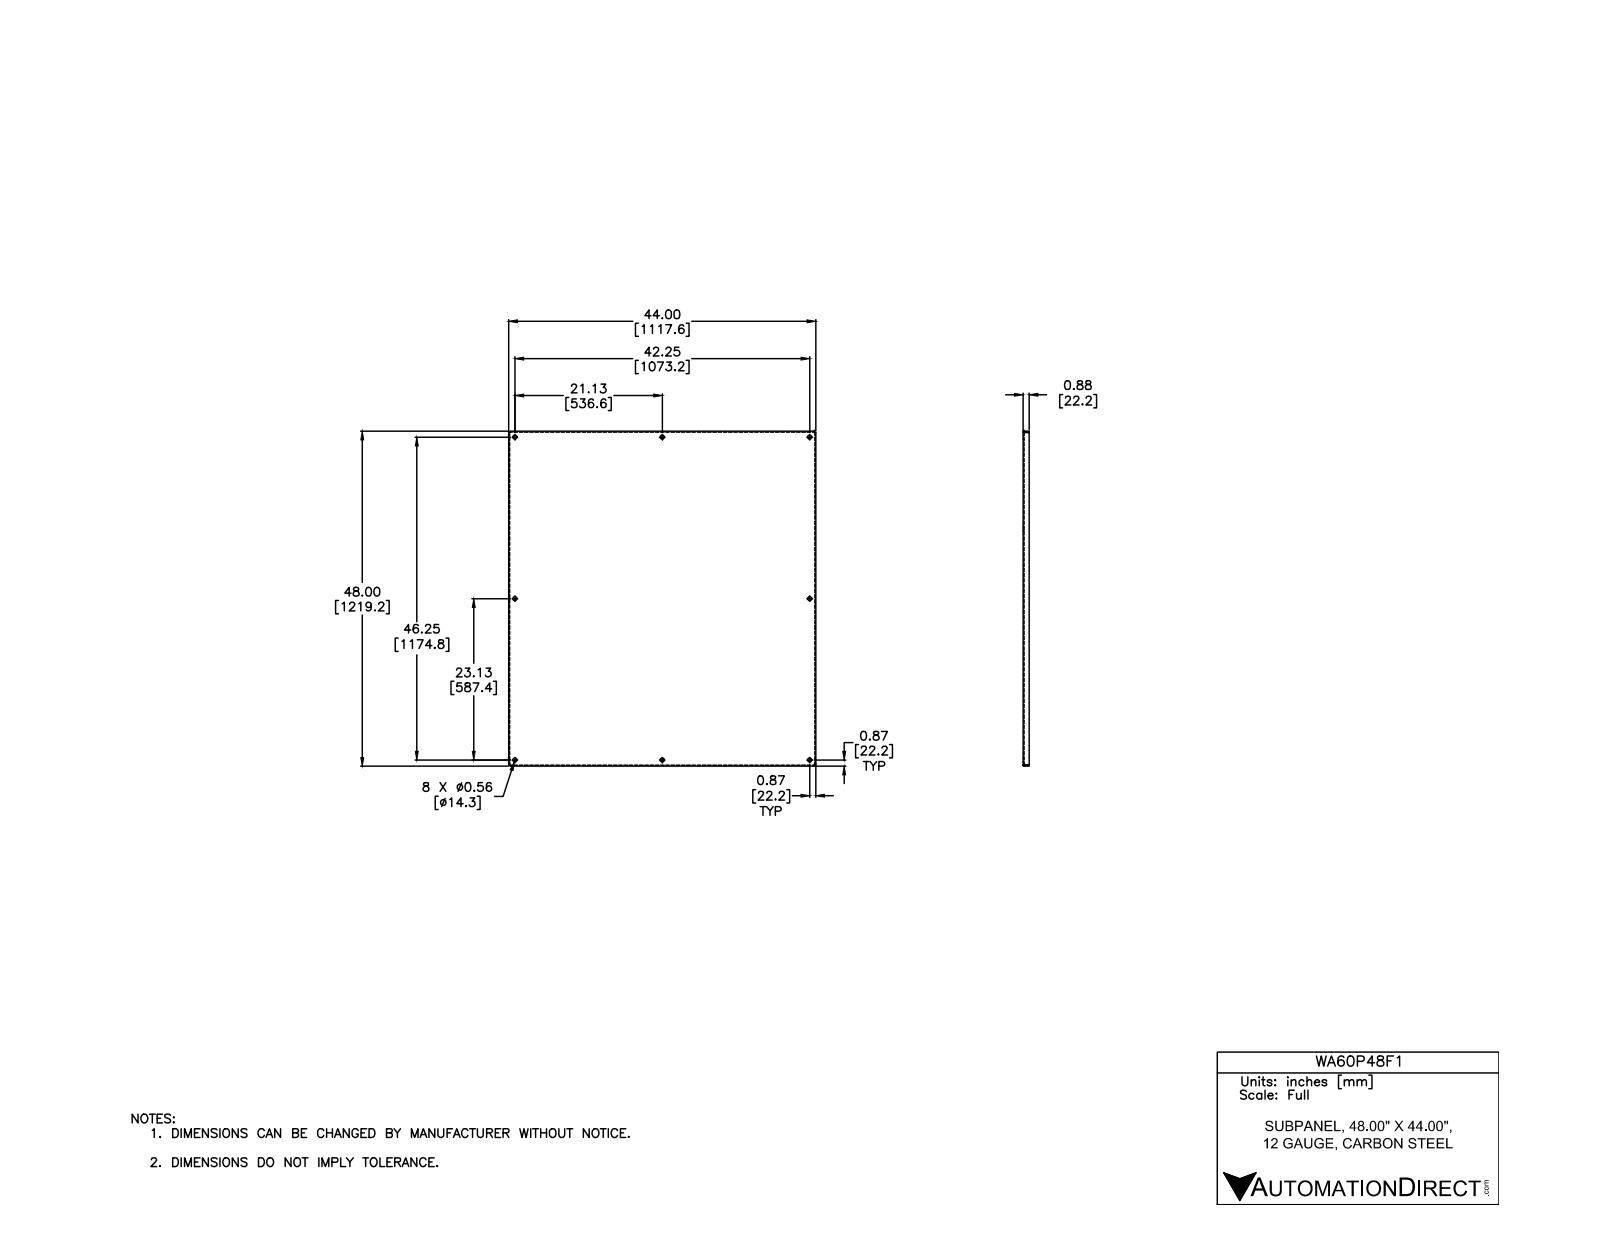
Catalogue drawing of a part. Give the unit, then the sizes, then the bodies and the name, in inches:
Units: inches
Overall size (bounding box): 48 × 44 × 0.875
Round holes (diameter × count): ⌀0.563 ×8
Partial cylindrical surfaces — rounded edges, fillets, slot ends (radius × count): R0.031 ×4, R0.156 ×4
Main face-to-face distances: 0.125, 47.875, 0.125, 44, 43.875, 43.875, 43.75, 48, 47.75, 0.75
Hole centre spacings: 21.125, 31.322, 48.165, 42.25, 23.125, 23.125, 46.25, 50.846
Volume: 279.9 in³ · Surface area: 4 504 in²
Bodies: 1 solid, 46 faces (22 planar, 16 cylindrical, 8 other)
Part name (STEP PRODUCT): WA_P_F
STEP written by: Autodesk Inventor 2012 (AUTOMOTIVE_DESIGN)
